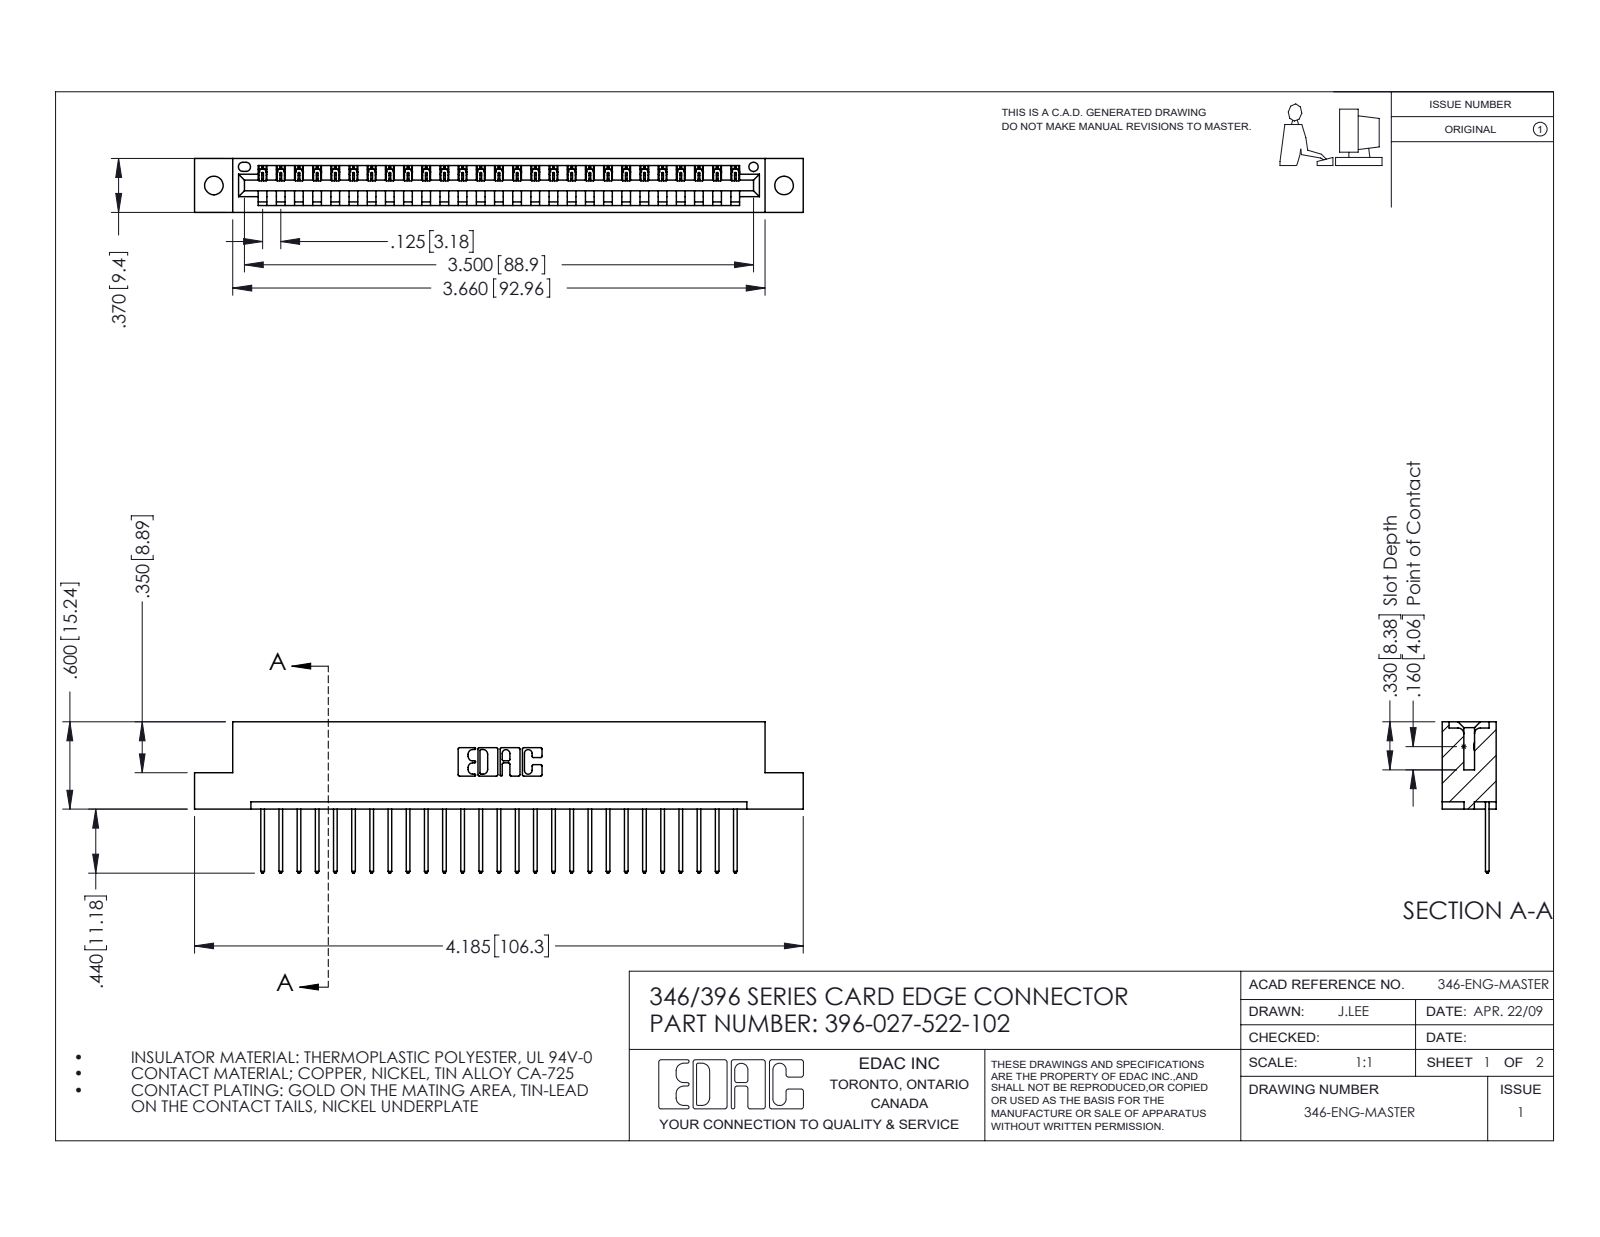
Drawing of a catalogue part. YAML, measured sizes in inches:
part_name: "345-292-001_345-293-122; 346 Part_Flush Mounting Lugs - 0.128 Dia; 396-027-522-102"
step_written_by: "SolidWorks 2016 (CONFIG_CONTROL_DESIGN)"
units: inches
bodies: {solids: 28, faces: 1688, planar: 1156, cylindrical: 532, other: 0}
overall_size: [4.185, 1.04, 0.37]
volume: 0.613
surface_area: 18.93
round_holes:
  - {diameter: 0.128, count: 2}
  - {diameter: 0.064, count: 1}
partial_cylinders:
  - {radius: 0.006, count: 54}
  - {radius: 0.01, count: 54}
  - {radius: 0.01, count: 22}
  - {radius: 0.007, count: 6}
  - {radius: 0.031, count: 6}
  - {radius: 0.026, count: 3}
  - {radius: 0.031, count: 2}
  - {radius: 0.04, count: 2}
face_to_face_distances: [0.048, 0.322, 0.25, 0.37, 0.072, 0.298, 0.025, 0.148, 0.222, 0.1]
hole_center_spacings: [0.246, 3.712, 3.92]
